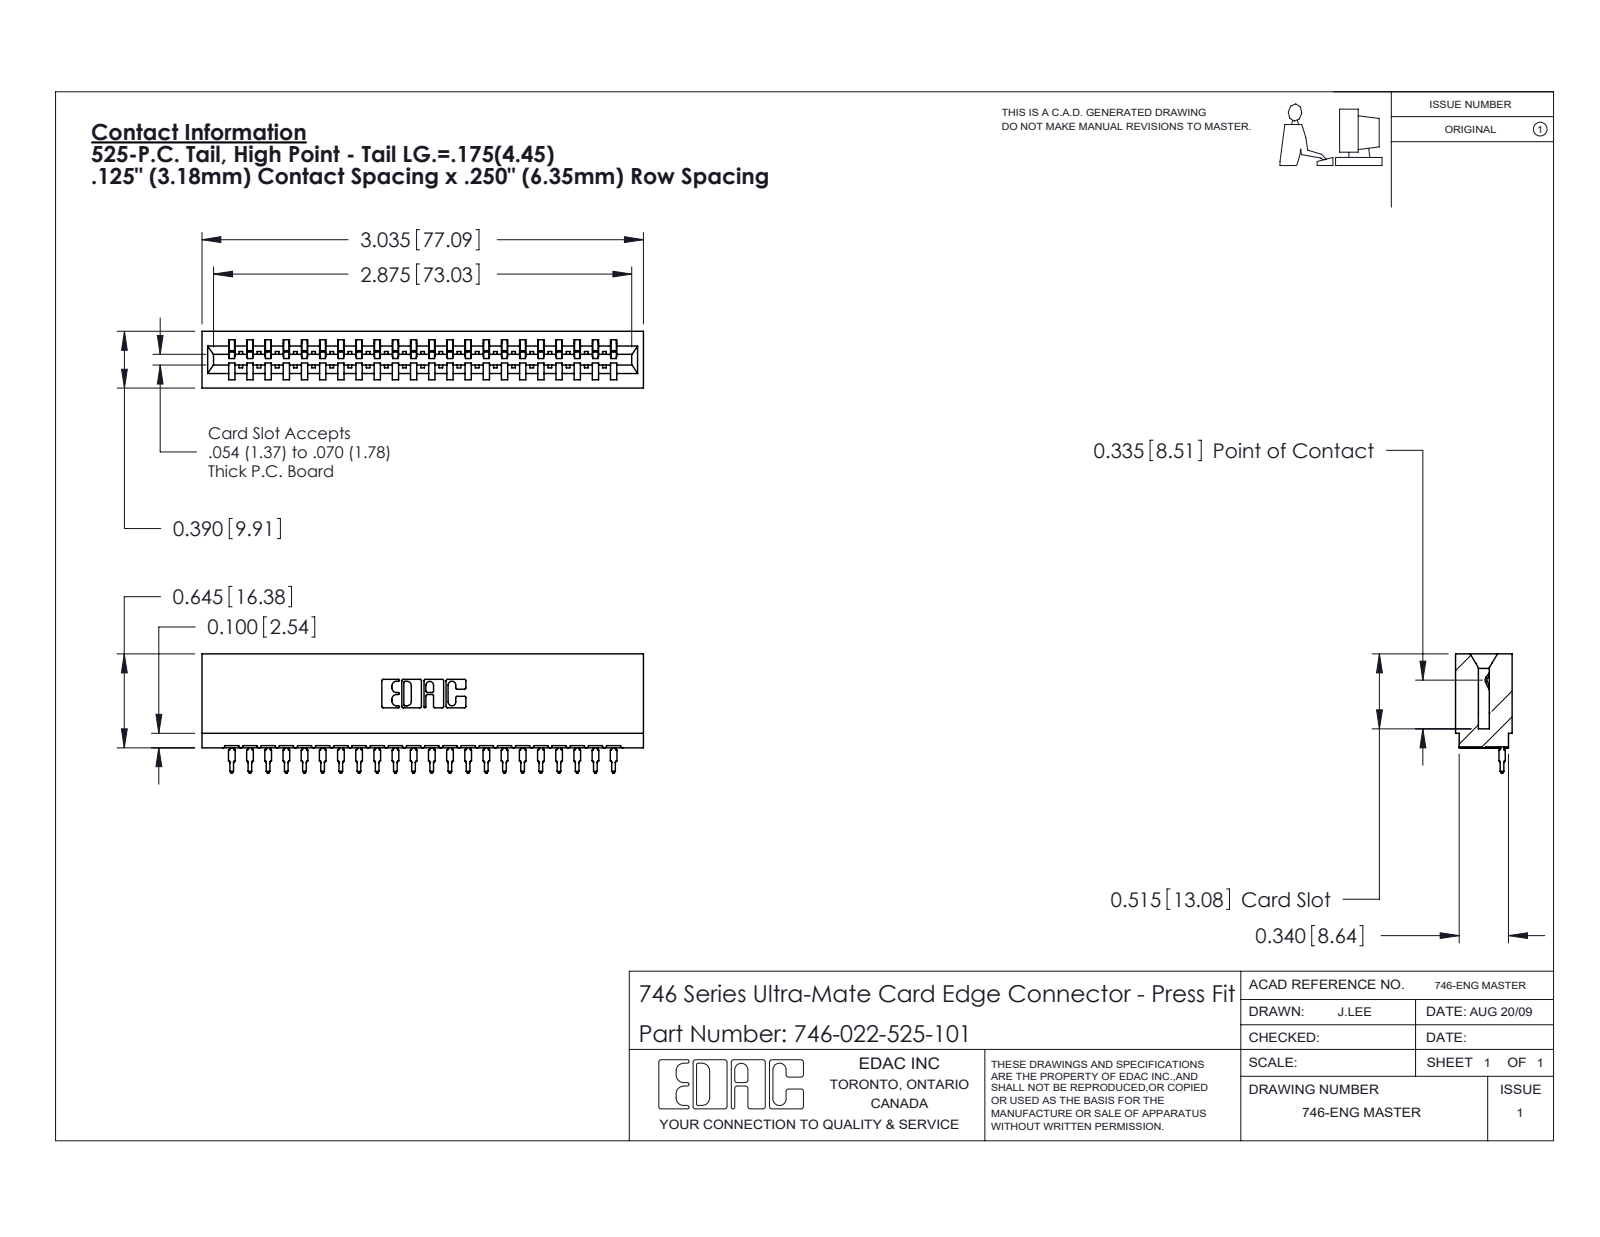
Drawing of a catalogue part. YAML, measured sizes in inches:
part_name: "746 Part_.515 Slot Depth - 01; 746-292-001_525; 746-022-525-101"
step_written_by: "SolidWorks 2020 (CONFIG_CONTROL_DESIGN)"
units: inches
bodies: {solids: 23, faces: 2473, planar: 1441, cylindrical: 460, other: 572}
overall_size: [3.035, 0.819, 0.39]
volume: 0.498
surface_area: 18.07
partial_cylinders:
  - {radius: 0.021, count: 44}
  - {radius: 0.015, count: 23}
  - {radius: 0.01, count: 22}
  - {radius: 0.007, count: 6}
  - {radius: 0.031, count: 6}
  - {radius: 0.005, count: 4}
  - {radius: 0.011, count: 4}
  - {radius: 0.026, count: 3}
face_to_face_distances: [0.057, 0.333, 0.25, 0.39, 0.5, 0.025, 0.307, 0.125, 0.125, 0.375]
